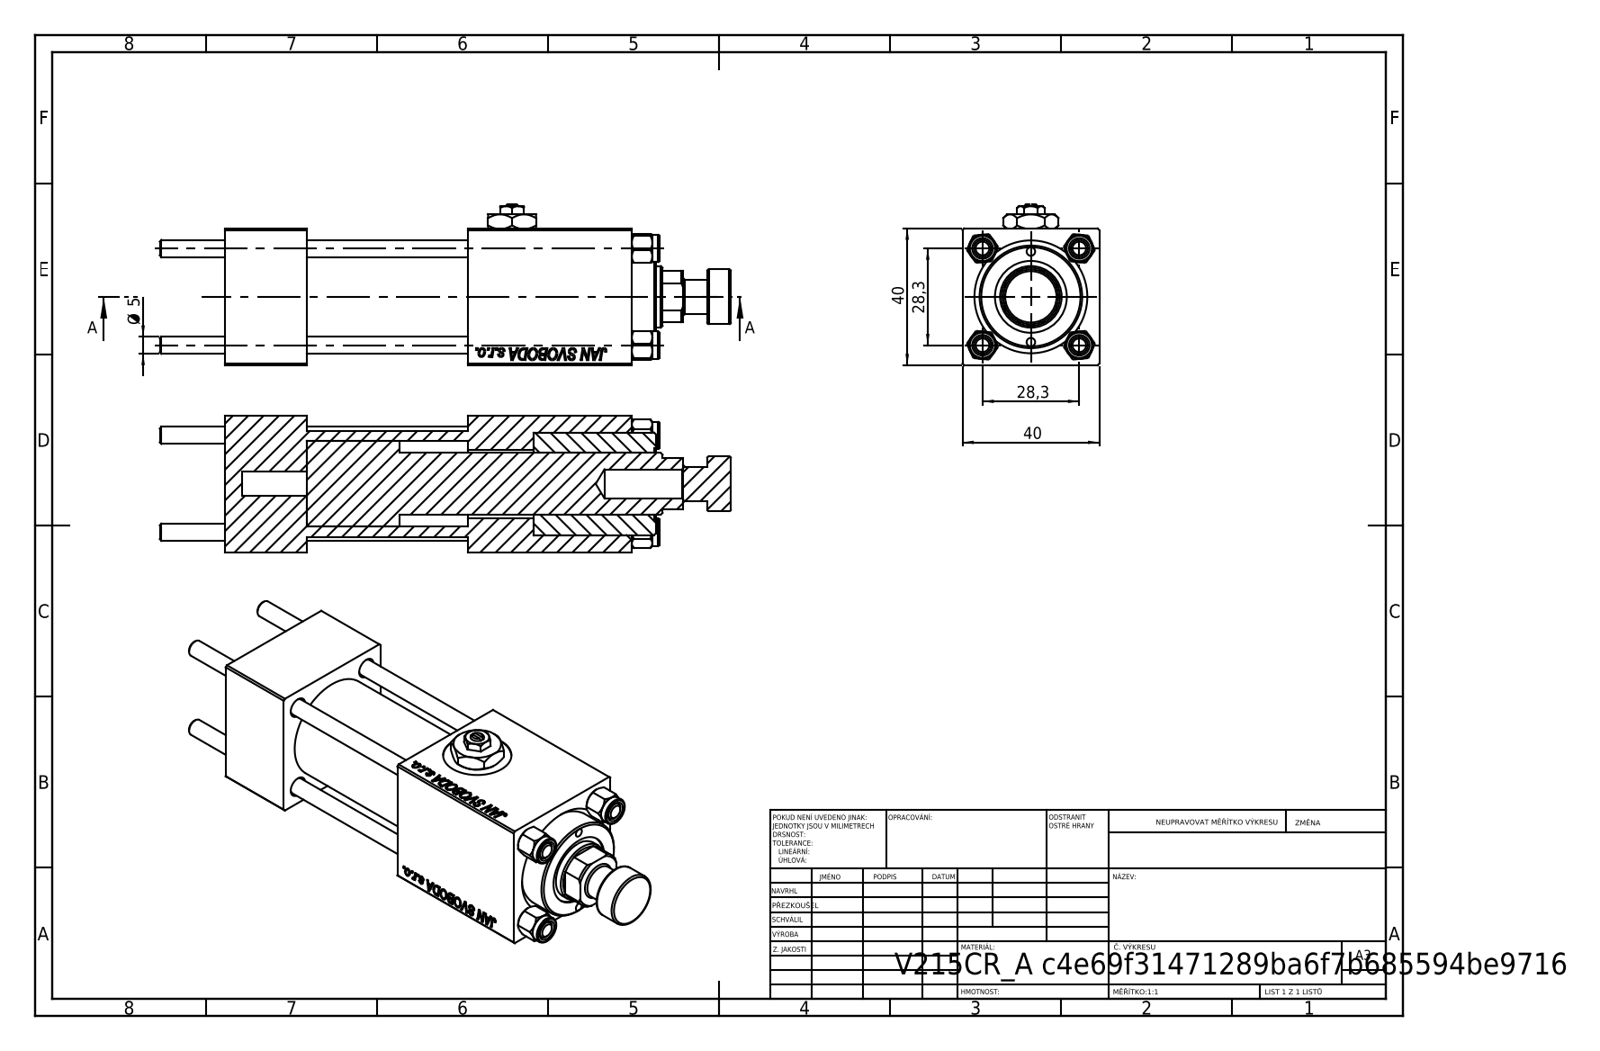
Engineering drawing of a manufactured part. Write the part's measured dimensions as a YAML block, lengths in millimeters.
part_name: "V215CR_VCP; NUT_M5; V215CR_ROD_END_W; Zatka_pro_OIL_PORT (+3 more)"
step_written_by: "SolidWorks 2019 (CONFIG_CONTROL_DESIGN)"
units: millimeters
bodies: {solids: 13, faces: 1195, planar: 545, cylindrical: 88, other: 562}
overall_size: [167, 47, 40]
volume: 153618
surface_area: 63055
round_holes:
  - {diameter: 5, count: 4}
  - {diameter: 20, count: 3}
  - {diameter: 2.5, count: 2}
  - {diameter: 7, count: 2}
  - {diameter: 13.16, count: 2}
  - {diameter: 8.5, count: 1}
  - {diameter: 18, count: 1}
  - {diameter: 21, count: 1}
  - {diameter: 25, count: 1}
  - {diameter: 30, count: 1}
round_bosses_or_shafts:
  - {diameter: 8, count: 4}
  - {diameter: 31, count: 1}
  - {diameter: 16, count: 1}
  - {diameter: 10, count: 1}
partial_cylinders:
  - {radius: 8.5, count: 1}
face_to_face_distances: [40, 24, 71, 47, 90.3, 66.3, 19.3, 119, 95, 48]
hole_center_spacings: [14.18, 20.01, 28.3, 30.84, 13.25, 40.02, 26.5, 72]
